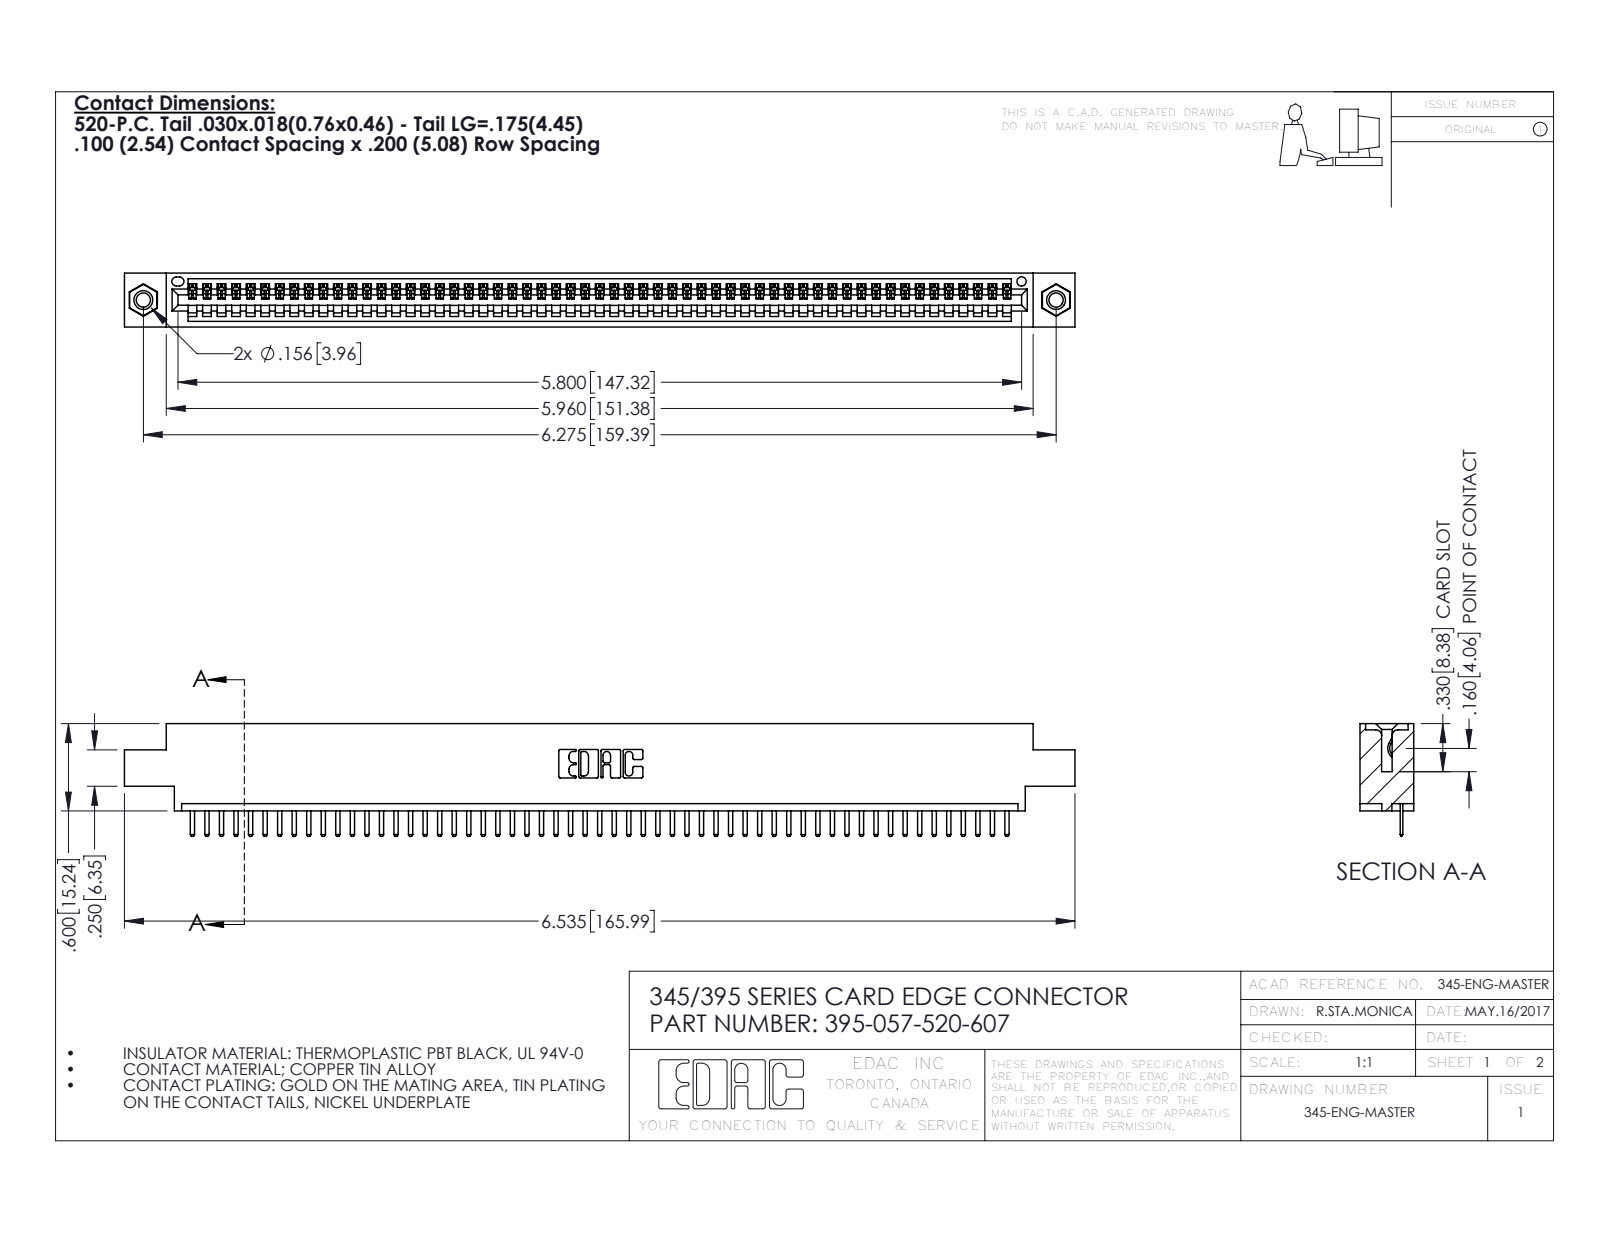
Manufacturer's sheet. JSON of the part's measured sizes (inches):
{"part_name": "345-292-001_345-293-120; 395-057-520-607; 345-250-001_345-250-005-103; 345 Part_0.170 Offset - 0.156 Dia-TI", "step_written_by": "SolidWorks 2016 (CONFIG_CONTROL_DESIGN)", "units": "inches", "bodies": {"solids": 60, "faces": 3724, "planar": 2510, "cylindrical": 1198, "other": 16}, "overall_size": [6.535, 0.775, 0.37], "volume_in3": 0.952, "surface_area_in2": 31.86, "round_holes": [[0.098, 2], [0.125, 2], [0.156, 2], [0.064, 1]], "round_bosses_or_shafts": [[0.155, 2]], "partial_cylinders_radius": [[0.01, 116], [0.006, 114], [0.01, 22], [0.007, 6], [0.031, 6], [0.026, 3], [0.031, 2], [0.04, 2]], "face_to_face_distances": [0.072, 0.298, 0.37, 0.2, 0.098, 0.272, 0.025, 0.225, 0.072, 0.175], "hole_center_spacings": [0.27, 6.039, 6.275]}
